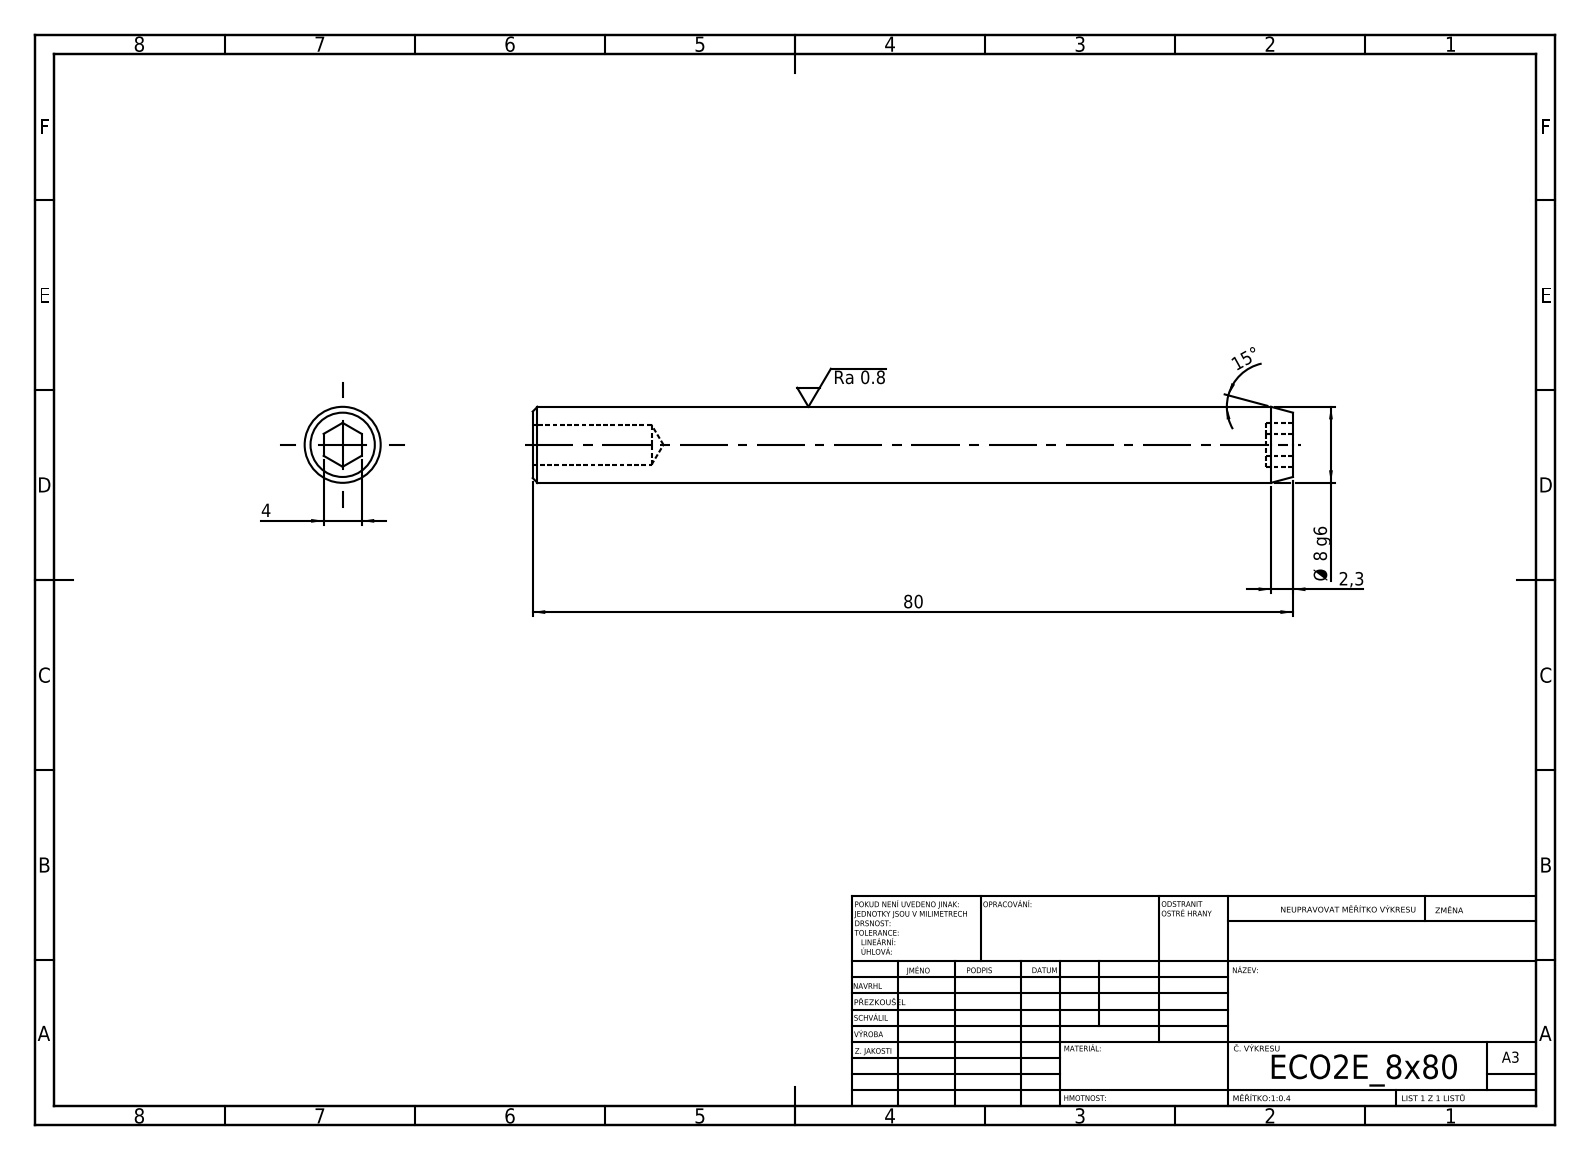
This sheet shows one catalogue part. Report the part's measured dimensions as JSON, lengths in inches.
{"step_written_by": "SolidWorks 2019 (CONFIG_CONTROL_DESIGN)", "units": "inches", "bodies": {"solids": 1, "faces": 19, "planar": 9, "cylindrical": 4, "other": 6}, "overall_size": [3.15, 0.315, 0.315], "volume_in3": 0.231, "surface_area_in2": 3.554, "round_holes": [[0.165, 1]], "round_bosses_or_shafts": [[0.315, 1]], "face_to_face_distances": [3.15, 0.157, 0.11, 3.039]}
